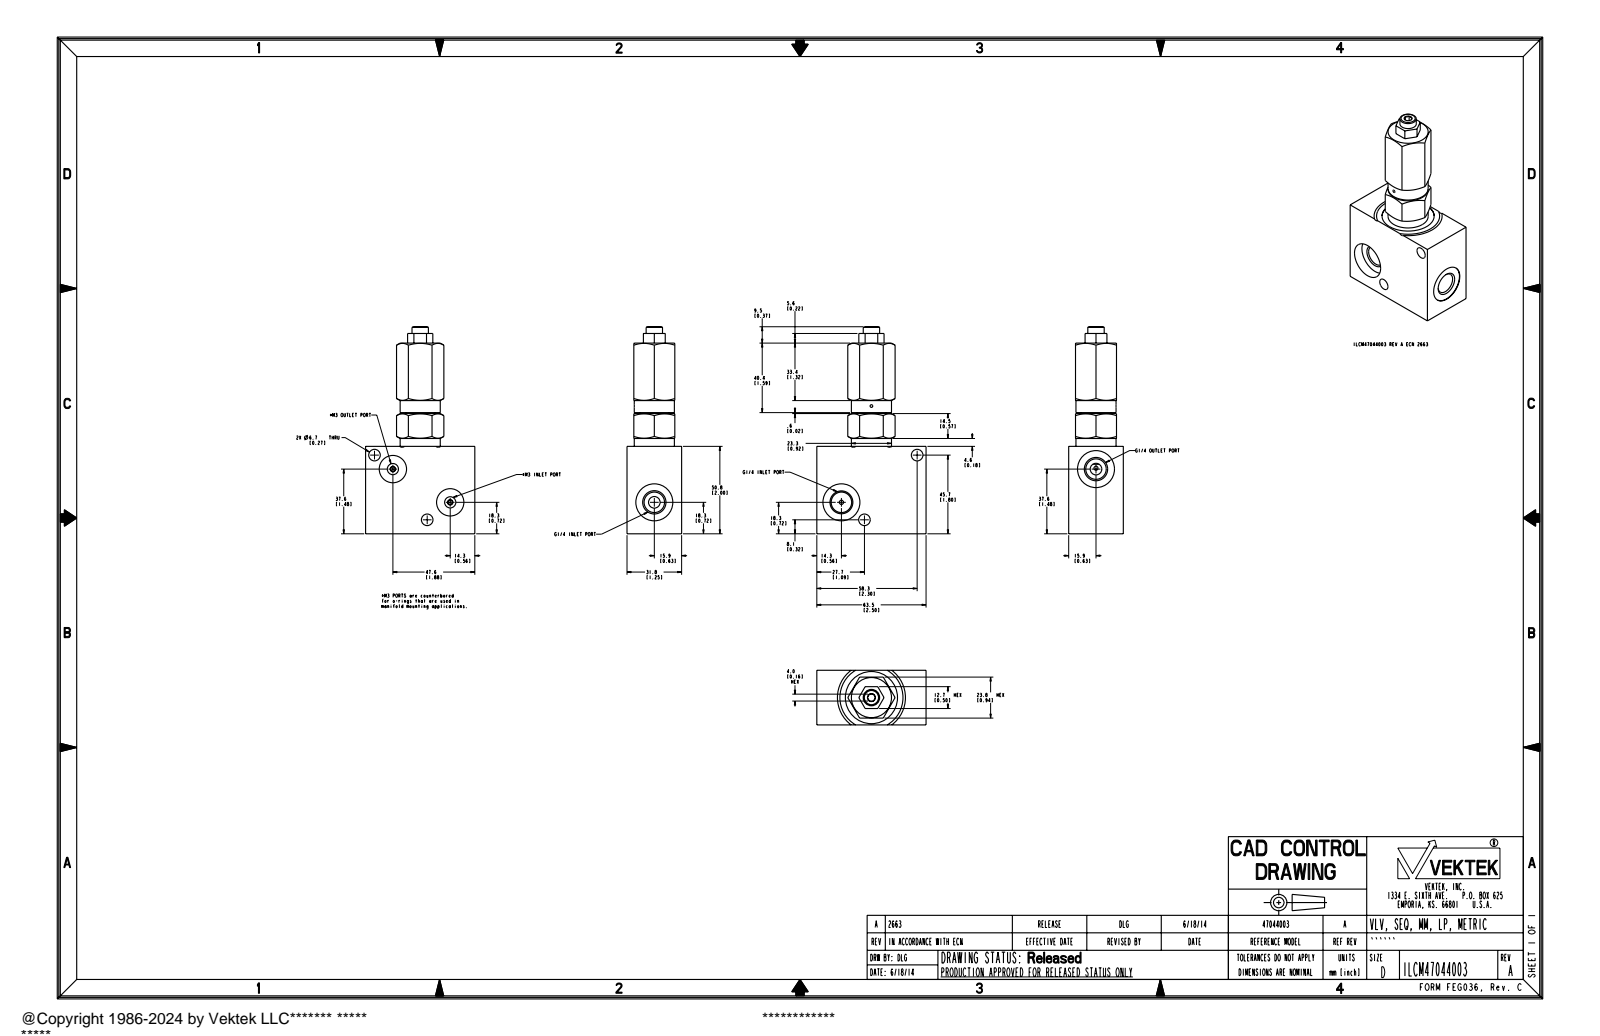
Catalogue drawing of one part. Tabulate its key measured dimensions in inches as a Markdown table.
| quantity | value |
| --- | --- |
| part name | ILCM47044003 |
| STEP written by | PRO/ENGINEER BY PARAMETRIC TECHNOLOGY CORPORATION, 2013320 (CONFIG_CONTROL_DESIGN) |
| units | inches |
| bodies | 1 solid, 174 faces (58 planar, 74 cylindrical, 42 other) |
| overall size | 4.736 × 2.5 × 1.25 |
| volume | 7.144 in³ |
| surface area | 41.1 in² |
| round holes (diameter × count) | 0.265 × 4, 0.468 × 3, 0.846 × 3, 0.094 × 2, 0.098 × 2, 0.125 × 2, 0.256 × 2, 0.625 × 2, 0.062 × 1, 0.203 × 1, 0.378 × 1, 0.592 × 1 |
| round bosses / shafts (diameter × count) | 0.918 × 1, 0.67 × 1, 0.587 × 1, 0.46 × 1, 0.375 × 1 |
| main face-to-face distances | 1.25, 0.938, 0.156, 1.094, 2.5, 2, 2.49, 0.105, 0.051, 0.989 |
| hole center spacings | 0.02, 0.529, 0.626, 0.662, 0.76, 0.78, 1.039, 1.088 |
